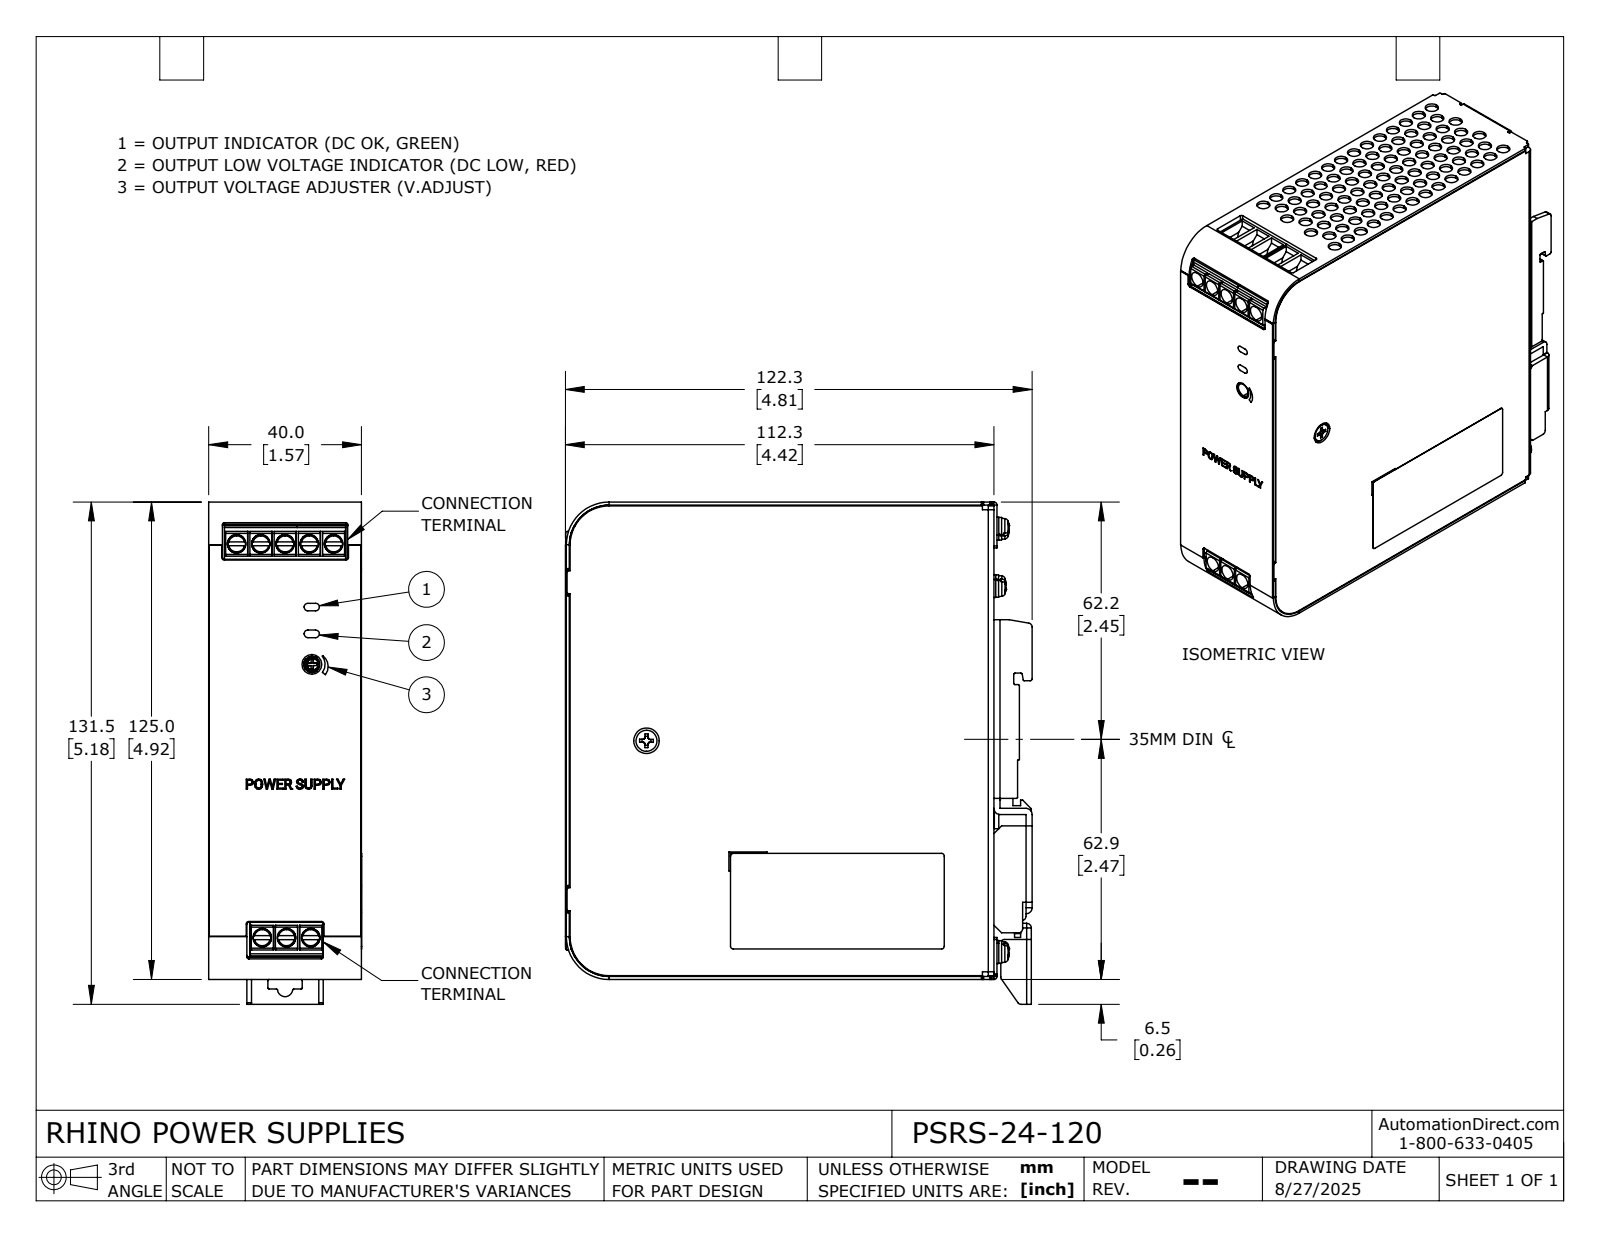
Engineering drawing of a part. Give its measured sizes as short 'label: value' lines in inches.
name: PSRS-24-120
written by: SolidWorks 2024 (AUTOMOTIVE_DESIGN)
unit: in
bodies: 2 solids, 2380 faces (1209 planar, 866 cylindrical, 305 other)
size: 5.177 × 4.813 × 1.577
volume: 34.17 in³; area: 112.4 in²
holes: 99× ⌀0.157, 10× ⌀0.142, 8× ⌀0.118, 8× ⌀0.122, 8× ⌀0.138, 8× ⌀0.183, 8× ⌀0.191, 3× ⌀0.098, 3× ⌀0.264, 2× ⌀0.059, 1× ⌀0.134, 1× ⌀0.165
bosses: 14× ⌀0.118, 8× ⌀0.236, 8× ⌀0.232, 8× ⌀0.187, 8× ⌀0.117, 3× ⌀0.217
rounds: 67× R0.012, 35× R0.02, 18× R0.006, 14× R0.039, 13× R0.063, 9× R0.004, 9× R0.047, 2× R0.024
face distances: 1.575, 0.031, 4.419, 0.063, 4.89, 4.921, 0.394, 0.331, 0.079, 0.047
hole spacings: 0.22, 0.461, 0.441, 0.406, 0.661, 0.599, 1.885, 2.104
